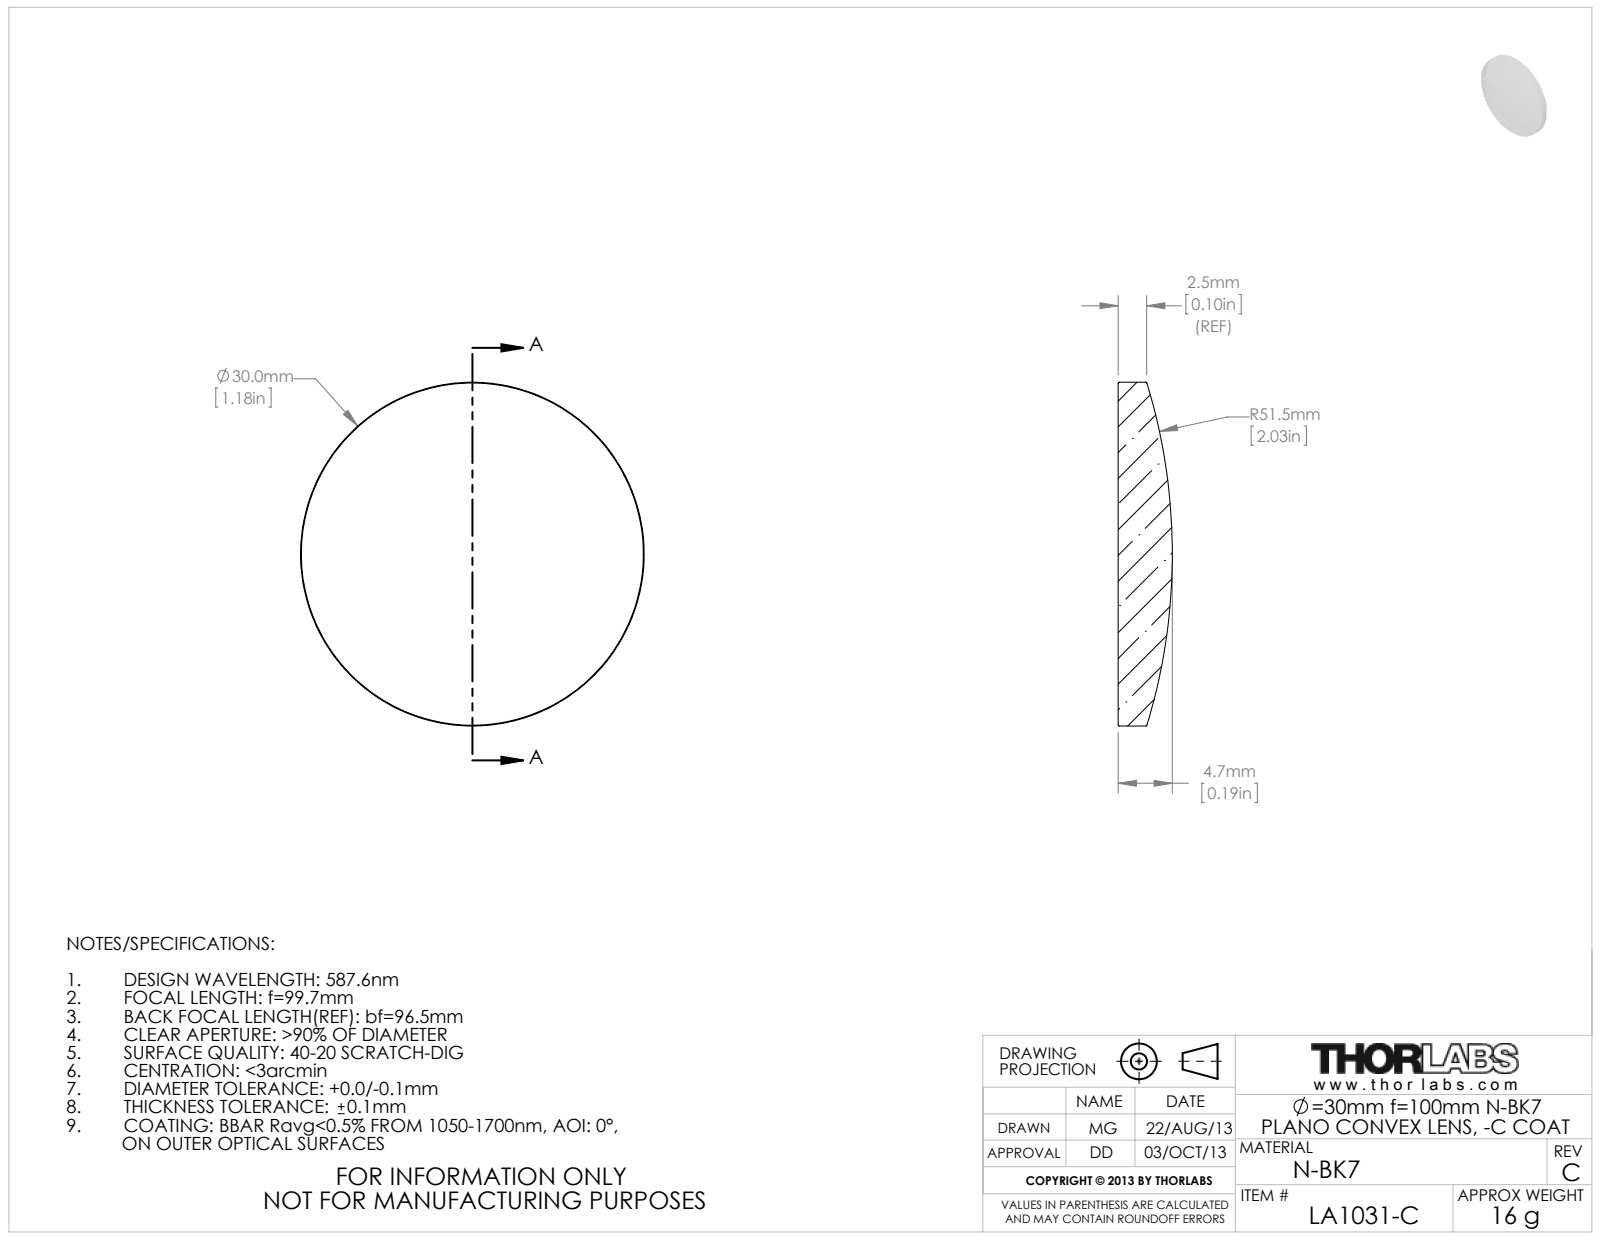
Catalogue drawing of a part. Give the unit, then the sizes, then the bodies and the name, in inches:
Units: inches
Overall size (bounding box): 1.181 × 1.181 × 0.186
Round bosses / shafts (diameter × count): ⌀1.181 ×1
Volume: 0.156 in³ · Surface area: 2.581 in²
Bodies: 1 solid, 5 faces (1 planar, 2 cylindrical, 2 other)
Part name (STEP PRODUCT): 4598-E0W
STEP written by: SolidWorks 2009 (AUTOMOTIVE_DESIGN)
